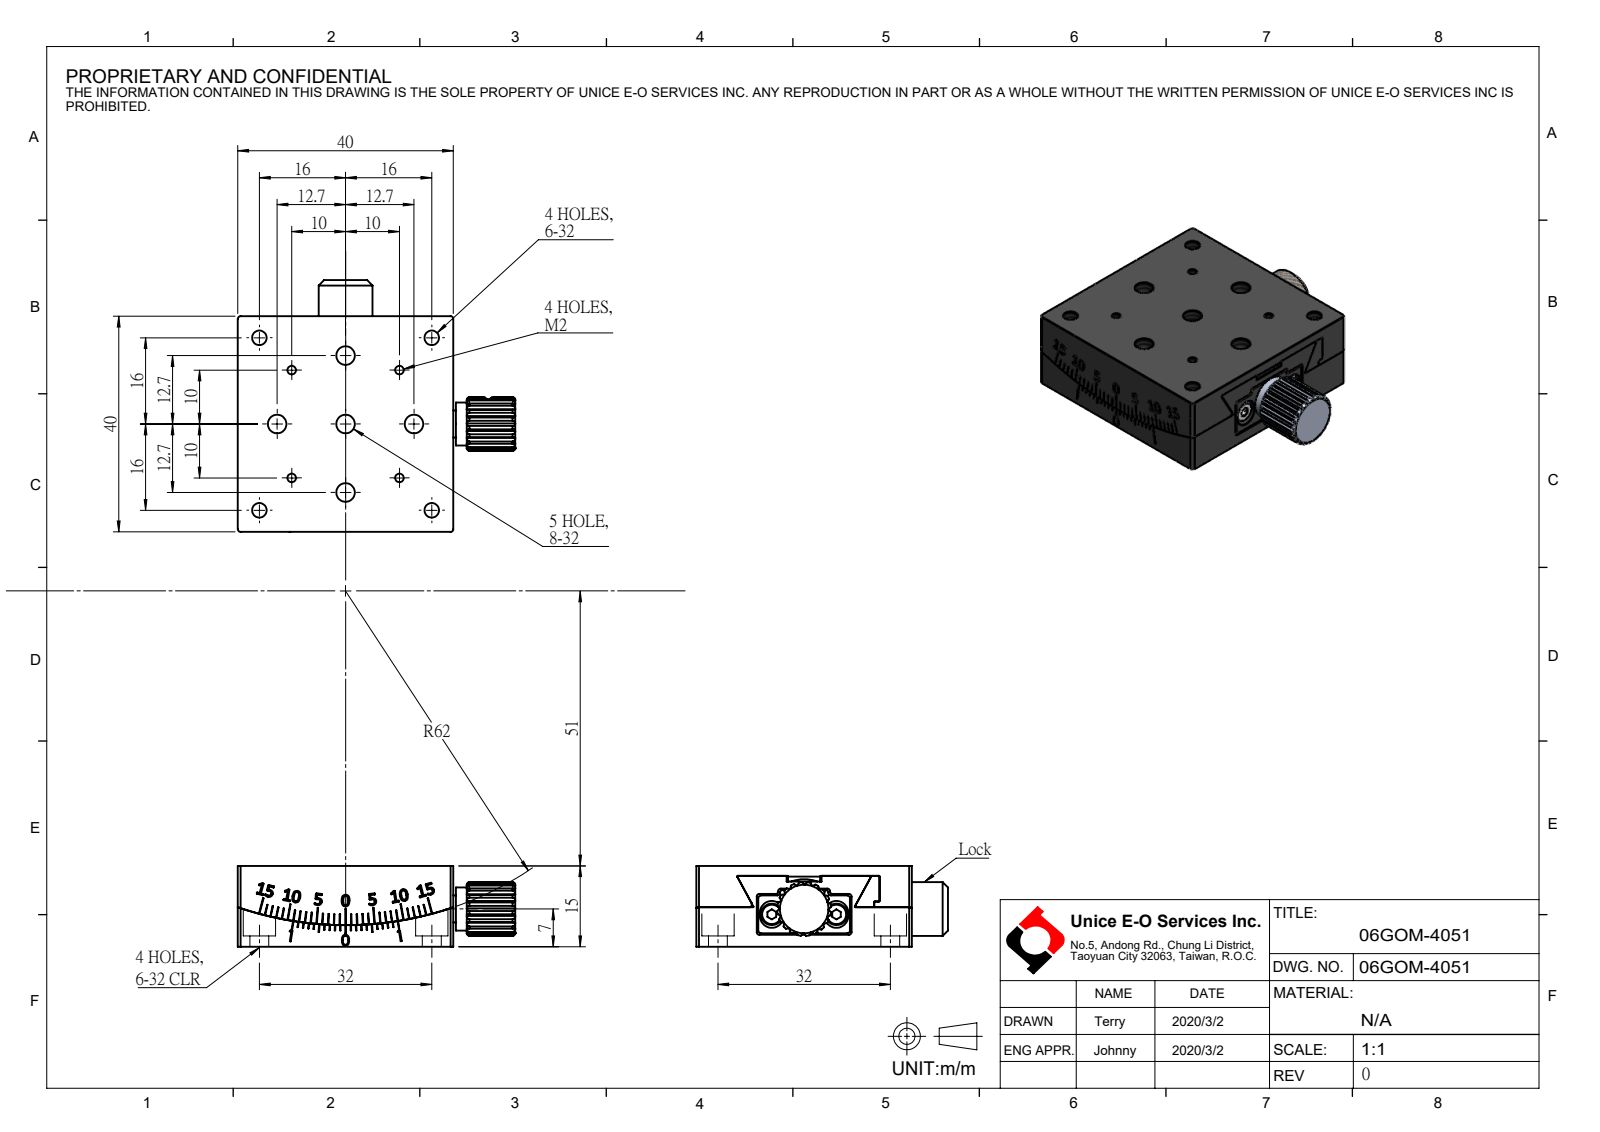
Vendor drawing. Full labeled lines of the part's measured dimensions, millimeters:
Part name (STEP PRODUCT): 06GOM-4051
STEP written by: SolidWorks 2016 (CONFIG_CONTROL_DESIGN)
Units: millimetres
Bodies: 0 solids, 608 faces (336 planar, 159 cylindrical, 113 other)
Overall size (bounding box): 51.5 × 46.7 × 15
Round holes (diameter × count): ⌀1.6 ×11, ⌀2.5 ×5, ⌀3.45 ×5, ⌀6 ×5, ⌀2.71 ×4, ⌀3.5 ×4
Round bosses / shafts (diameter × count): ⌀4 ×2, ⌀10 ×1, ⌀8 ×1
Partial cylindrical surfaces — rounded edges, fillets, slot ends (radius × count): R0.5 ×20, R2.2 ×4, R5 ×1, R56.5 ×1, R57.5 ×1, R62 ×1
Main face-to-face distances: 15, 40, 11.5, 2.5, 8.3, 12.5, 2.2, 12.8, 11.2, 17
Hole centre spacings: 10.36, 16.34, 24.81, 26.68, 32.86, 6, 6.69, 8.17
